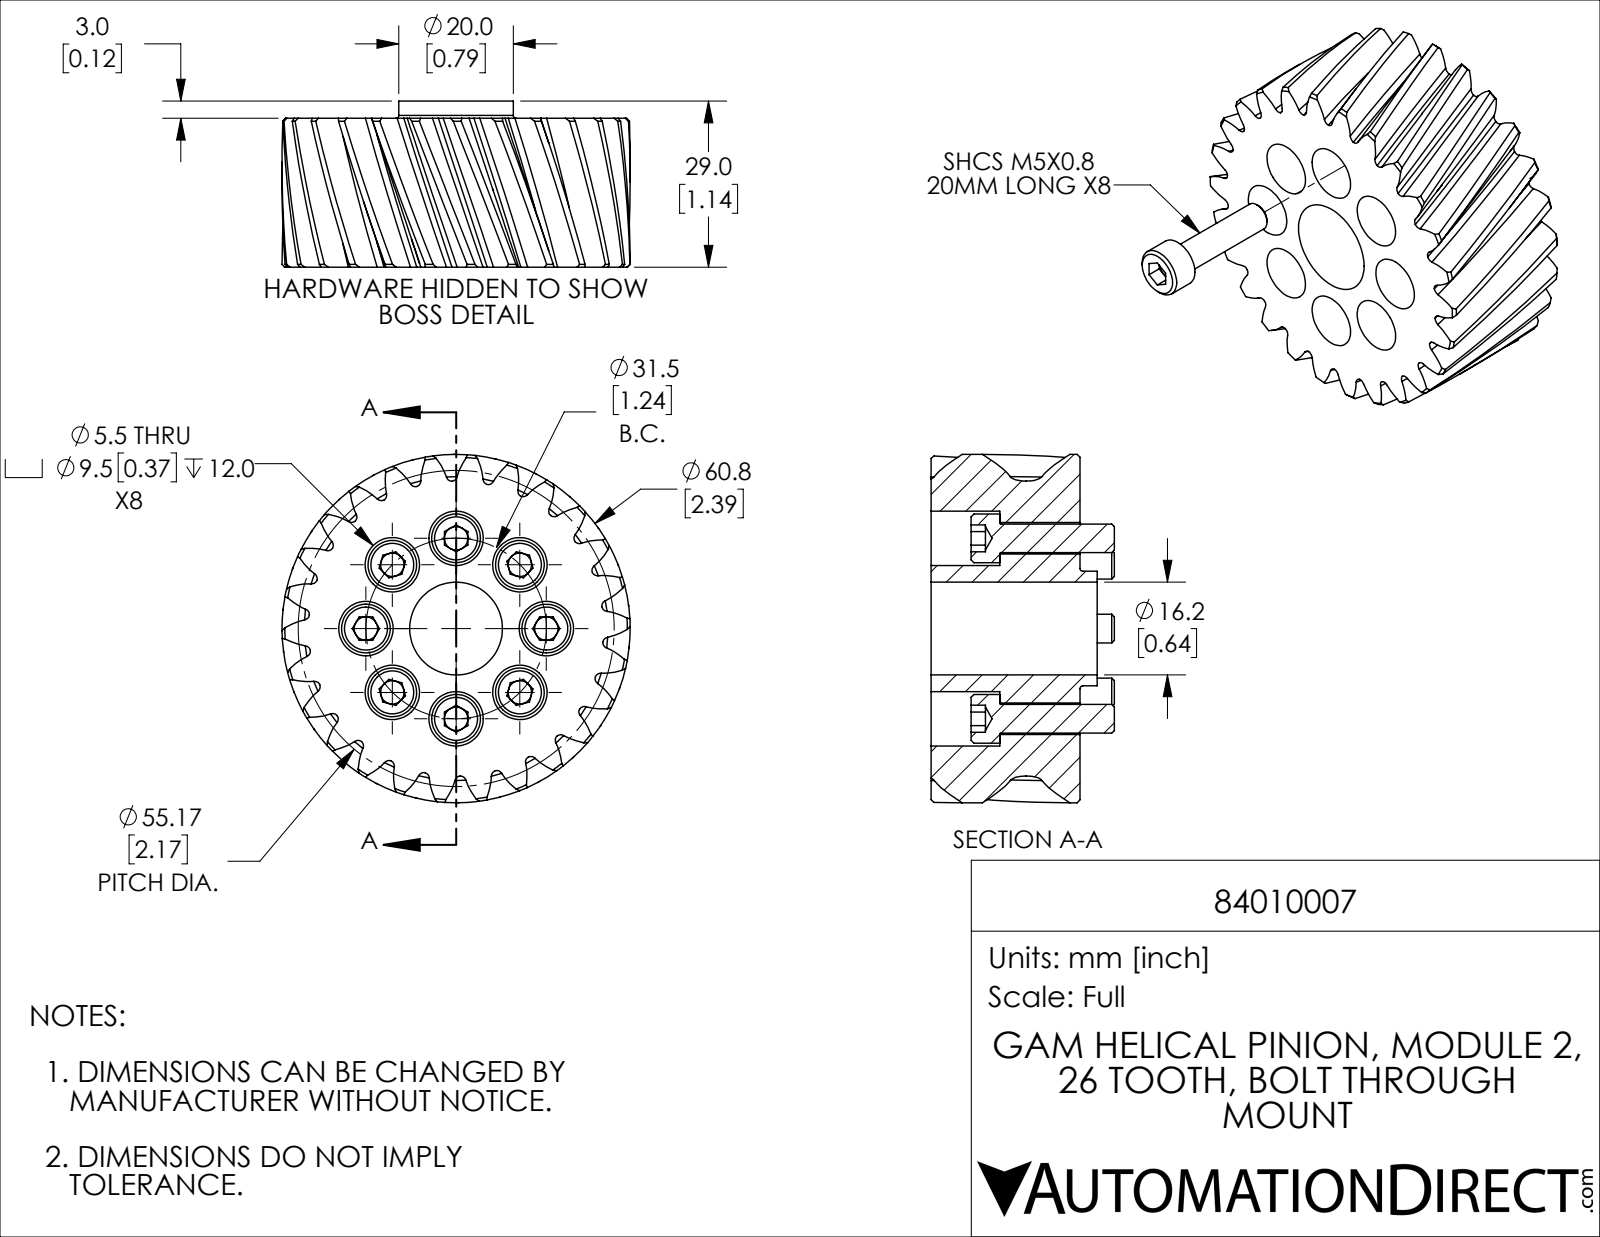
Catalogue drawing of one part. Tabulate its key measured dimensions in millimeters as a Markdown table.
| quantity | value |
| --- | --- |
| part name | 84010007 |
| STEP written by | SolidWorks 2019 (CONFIG_CONTROL_DESIGN) |
| units | millimeters |
| bodies | 9 solids, 449 faces (131 planar, 95 cylindrical, 223 other) |
| overall size | 60.8 × 60.8 × 32 |
| volume | 55 711 mm³ |
| surface area | 24 176 mm² |
| round holes (diameter × count) | 5.5 × 8, 9.5 × 8, 16.2 × 1 |
| round bosses / shafts (diameter × count) | 8.5 × 8, 5 × 8, 60.8 × 1, 20 × 1 |
| main face-to-face distances | 26, 12, 14, 7, 5, 19, 3, 29, 22, 17 |
| hole center spacings | 12.06, 15.75, 29.11, 22.27, 22.28, 31.5, 31.51 |
